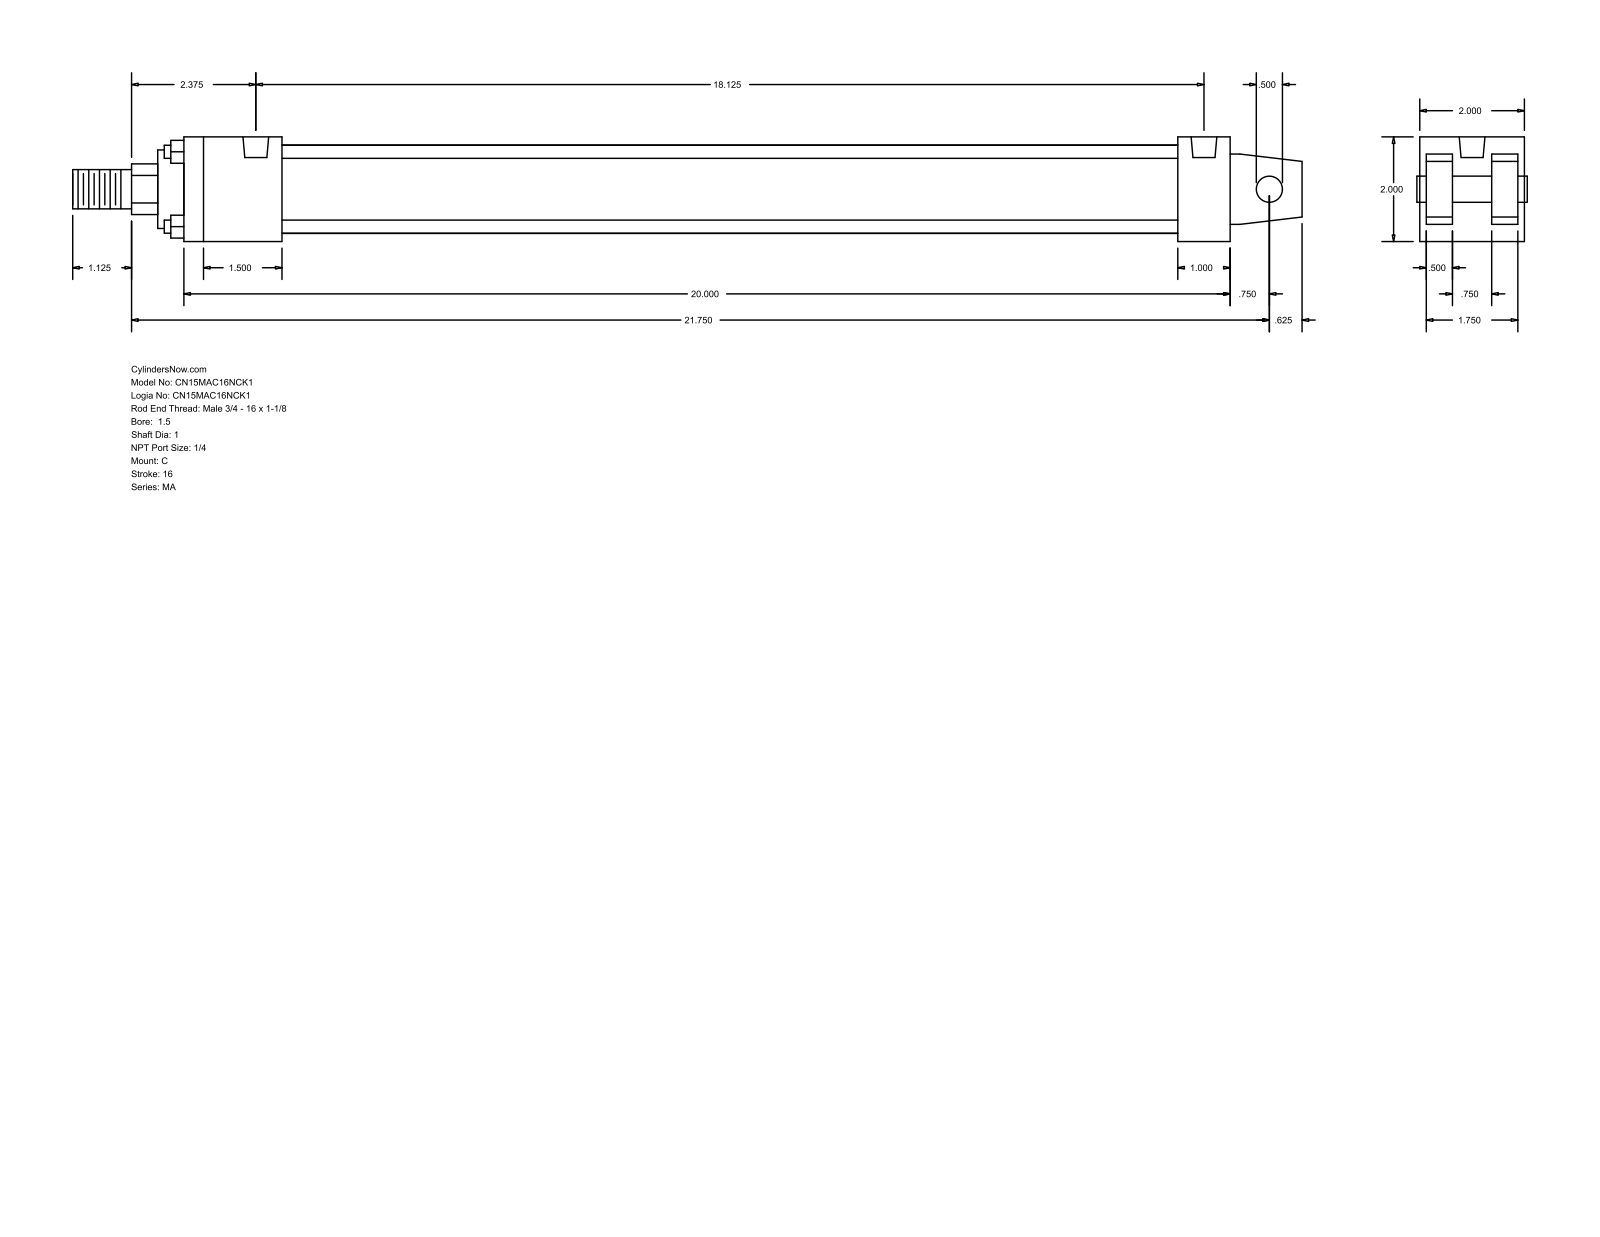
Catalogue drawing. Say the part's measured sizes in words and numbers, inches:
The part is named "MA_C__0150_1". Its 3-D file was written by "GSSL Pune (CONFIG_CONTROL_DESIGN)". It is 0 solids with 103 faces: 76 planar, 27 cylindrical and 0 other. Overall it measures 23.5 by 2 by 2 inches. Round holes: 4 of diameter 0.313, 2 of diameter 0.492. Round bosses or shafts: 4 of diameter 0.25, 1 of diameter 1.69, 1 of diameter 1.5, 1 of diameter 1, 1 of diameter 0.75, 1 of diameter 0.5. Partial cylindrical surfaces (rounded edges, fillets, slot ends): 1 of radius 0.484. The main face-to-face distances are 2, 1.875, 0.5, 1.375, 0.125, 0.625, 1.25, 2.375, 19.5, 20. The hole center spacings are 18.125.
